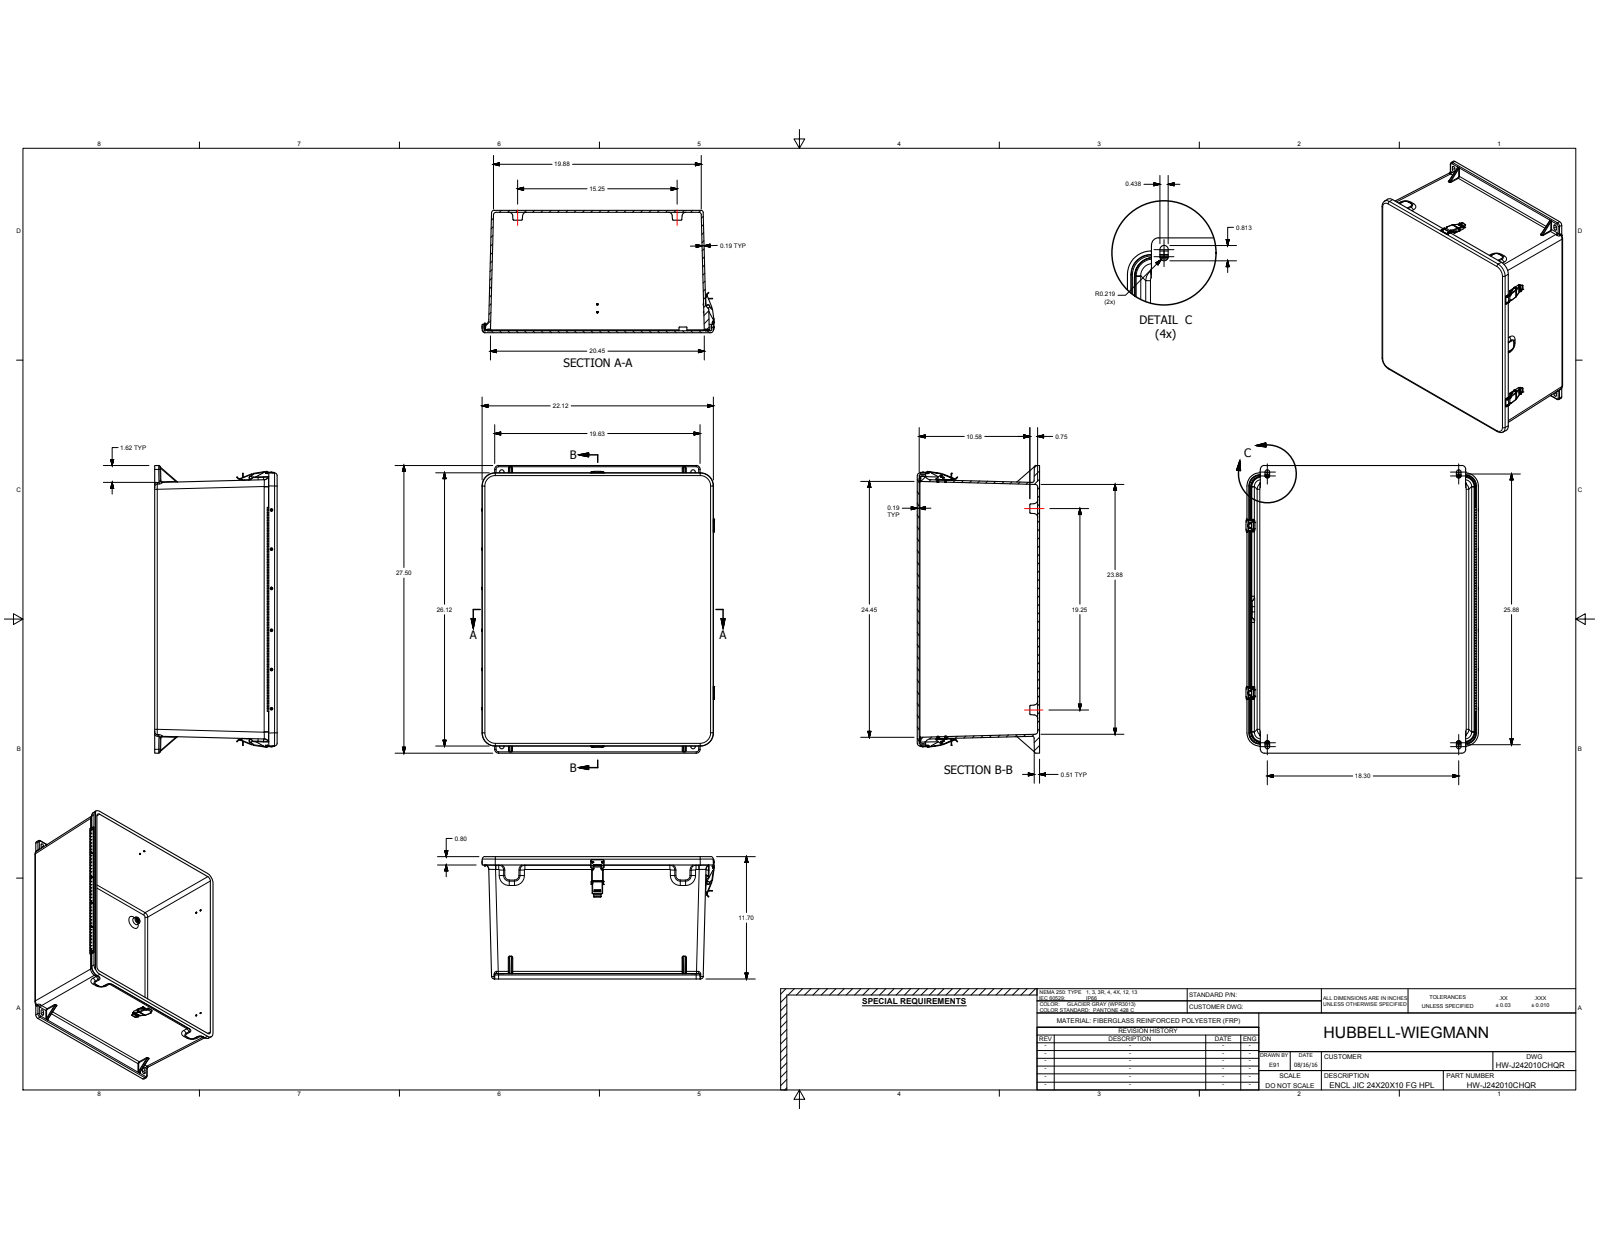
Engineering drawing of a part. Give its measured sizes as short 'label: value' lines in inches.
name: HW-J242010CHQR; WP2420H&LBOX; RMINS25020A12-18; RMLATPLSSL (+8 more)
written by: Autodesk Inventor 2017 (AUTOMOTIVE_DESIGN)
unit: in
bodies: 62 solids, 2139 faces (803 planar, 878 cylindrical, 458 other)
size: 27.5 × 22.224 × 11.701
volume: 462 in³; area: 4 653 in²
holes: 28× ⌀0.104, 24× ⌀0.139, 12× ⌀0.131, 8× ⌀0.13, 8× ⌀0.14, 6× ⌀0.135, 4× ⌀0.204, 4× ⌀0.313, 4× ⌀0.375, 2× ⌀0.31, 1× ⌀0.085
bosses: 28× ⌀0.125, 4× ⌀0.391, 3× ⌀0.3, 3× ⌀0.17, 3× ⌀0.12, 1× ⌀0.155
rounds: 72× R0.005, 44× R0.015, 40× R0.125, 34× R0.02, 32× R0.045, 28× R0.063, 24× R0.03, 22× R0.06
face distances: 0.188, 11.513, 11.701, 11.325, 0.188, 0.474, 11.438, 11.25, 0.075, 0.263
hole spacings: 3.75, 7.5, 0.937, 16, 11, 11.5, 7.25, 7.75
